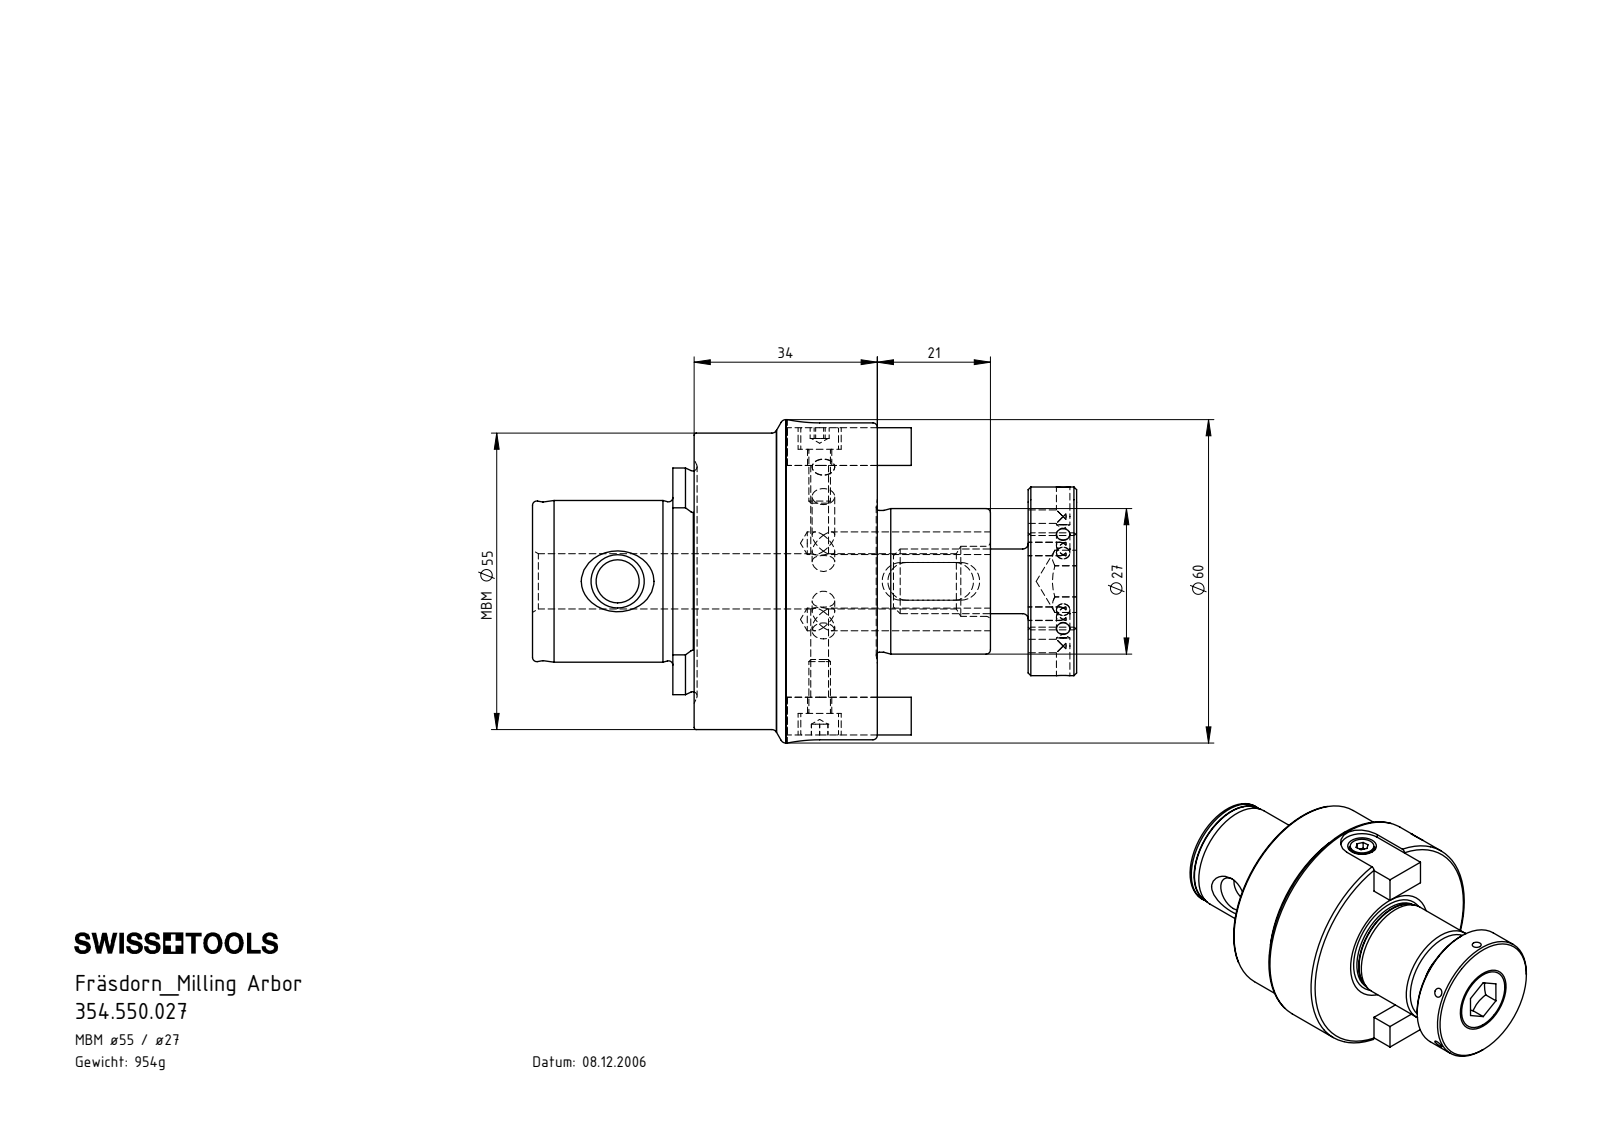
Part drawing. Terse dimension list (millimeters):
name: D27-ER2.002.012_A; ISO 4762 - M4 x 10; D27-ER1.K61.018; D27-ER1.K63.018_A (+4 more)
written by: SolidWorks 2017 (AUTOMOTIVE_DESIGN)
unit: mm
bodies: 8 solids, 213 faces (77 planar, 66 cylindrical, 70 other)
size: 101 × 60 × 60
volume: 125 987 mm³; area: 29 726 mm²
holes: 11× ⌀2.5, 3× ⌀4.2, 2× ⌀8, 1× ⌀3.3, 1× ⌀4.5, 1× ⌀10.25, 1× ⌀13, 1× ⌀17
bosses: 1× ⌀60, 1× ⌀55, 1× ⌀35, 1× ⌀30, 1× ⌀27, 1× ⌀26.3, 1× ⌀18, 1× ⌀12
rounds: 4× R3.5, 1× R6, 1× R21.02
face distances: 7, 37, 28, 34, 71, 62, 9, 25, 30, 64
hole spacings: 12, 20.79, 3.47, 8.64, 10, 13.46, 17.51, 20.33
